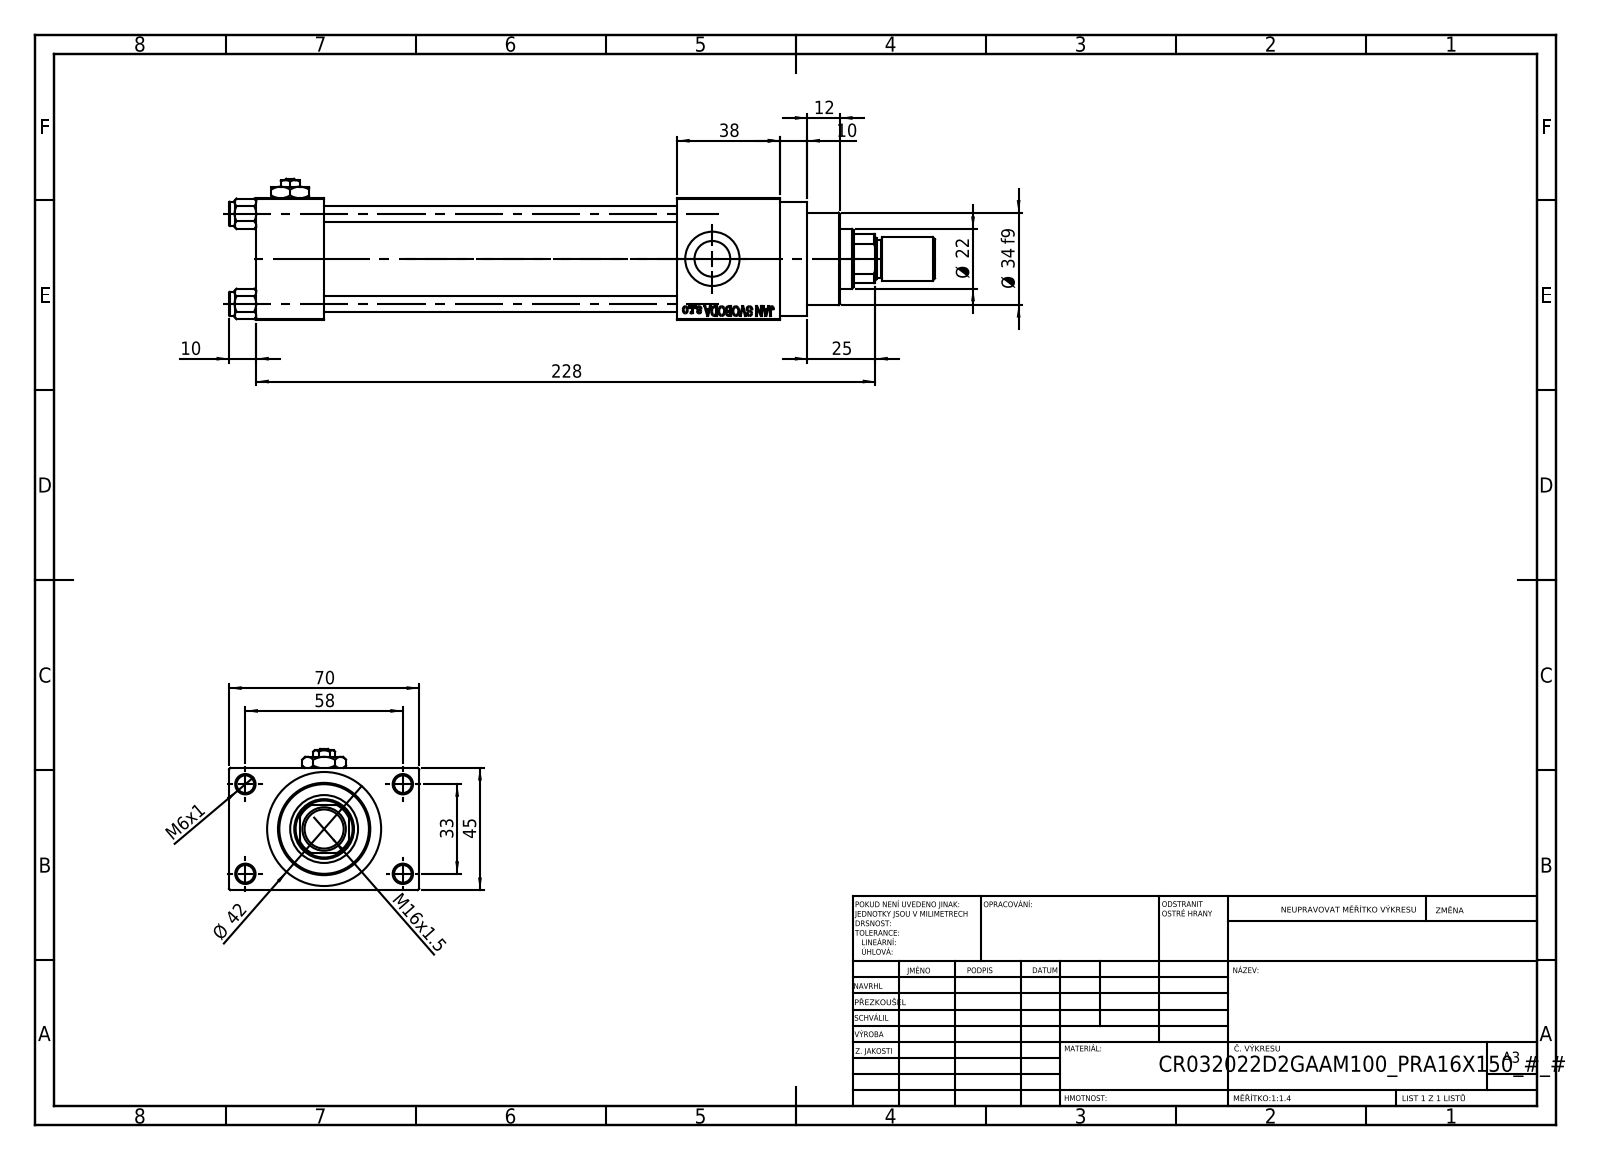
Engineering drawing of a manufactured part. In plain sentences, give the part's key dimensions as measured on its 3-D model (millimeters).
The part is named "V215CR_VCP_D; ROD_END_AH; V215CR_D_Body; V215_VC_A (+3 more)". Its 3-D file was written by "SolidWorks 2019 (CONFIG_CONTROL_DESIGN)". It is 13 solids with 1159 faces: 522 planar, 93 cylindrical and 544 other. Overall it measures 260 by 70 by 52 millimeters. Its volume is 313 893 cubic millimeters and its surface area 111 263 square millimeters. Round holes: 4 of diameter 6, 4 of diameter 6.5, 2 of diameter 7, 2 of diameter 13.16, 2 of diameter 20, 1 of diameter 10.5, 1 of diameter 22, 1 of diameter 24, 1 of diameter 25, 1 of diameter 32, 1 of diameter 33. Round bosses or shafts: 4 of diameter 9, 1 of diameter 42, 1 of diameter 38, 1 of diameter 34, 1 of diameter 16, 1 of diameter 14. Partial cylindrical surfaces (rounded edges, fillets, slot ends): 1 of radius 10.5. The main face-to-face distances are 45, 25, 12.5, 57.5, 130, 155, 168, 38, 193, 70. The hole center spacings are 12.4, 23.48, 33.2, 33.37, 35.35, 45.6, 56.35, 33.
